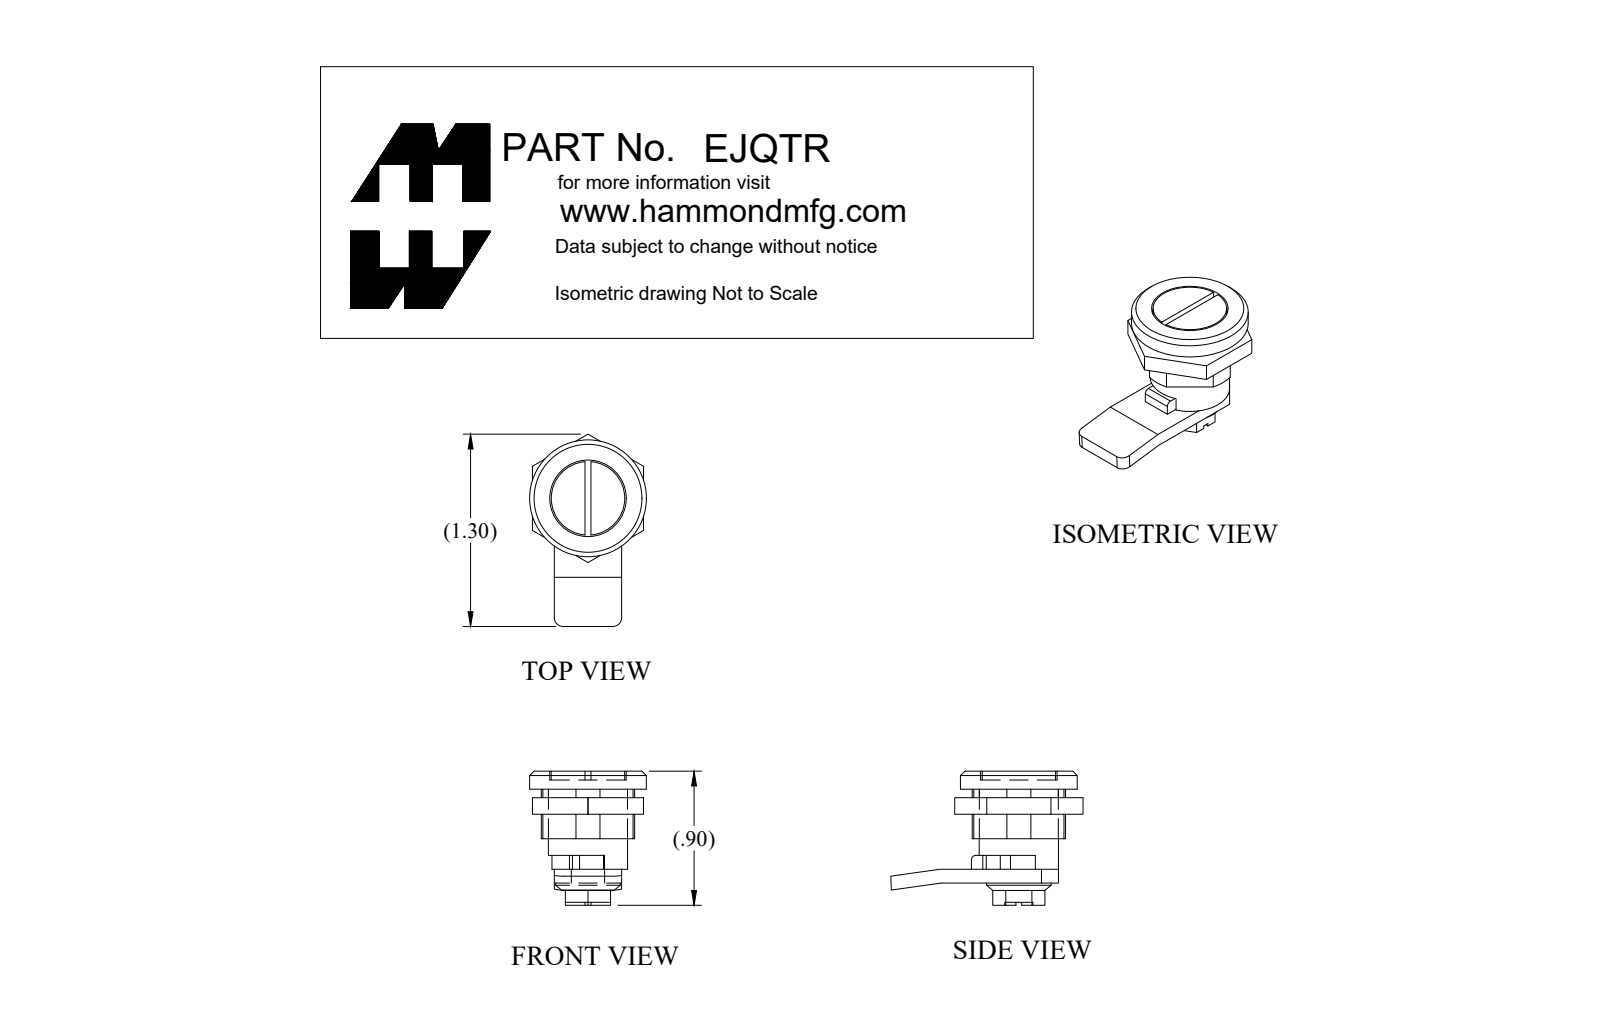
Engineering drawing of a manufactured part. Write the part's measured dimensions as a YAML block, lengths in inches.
part_name: "EJQTR_Default"
step_written_by: "SolidWorks 2019 (CONFIG_CONTROL_DESIGN)"
units: inches
bodies: {solids: 1, faces: 100, planar: 71, cylindrical: 25, other: 4}
overall_size: [1.298, 0.905, 0.788]
volume: 0.273
surface_area: 4.18
round_holes:
  - {diameter: 0.516, count: 1}
round_bosses_or_shafts:
  - {diameter: 0.788, count: 1}
  - {diameter: 0.535, count: 1}
  - {diameter: 0.496, count: 1}
  - {diameter: 0.435, count: 1}
partial_cylinders:
  - {radius: 0.06, count: 2}
  - {radius: 0.03, count: 1}
  - {radius: 0.125, count: 1}
  - {radius: 0.315, count: 1}
face_to_face_distances: [0.093, 0.122, 0.057, 0.179, 0.112, 0.169, 0.291, 0.371, 0.483, 0.54]
